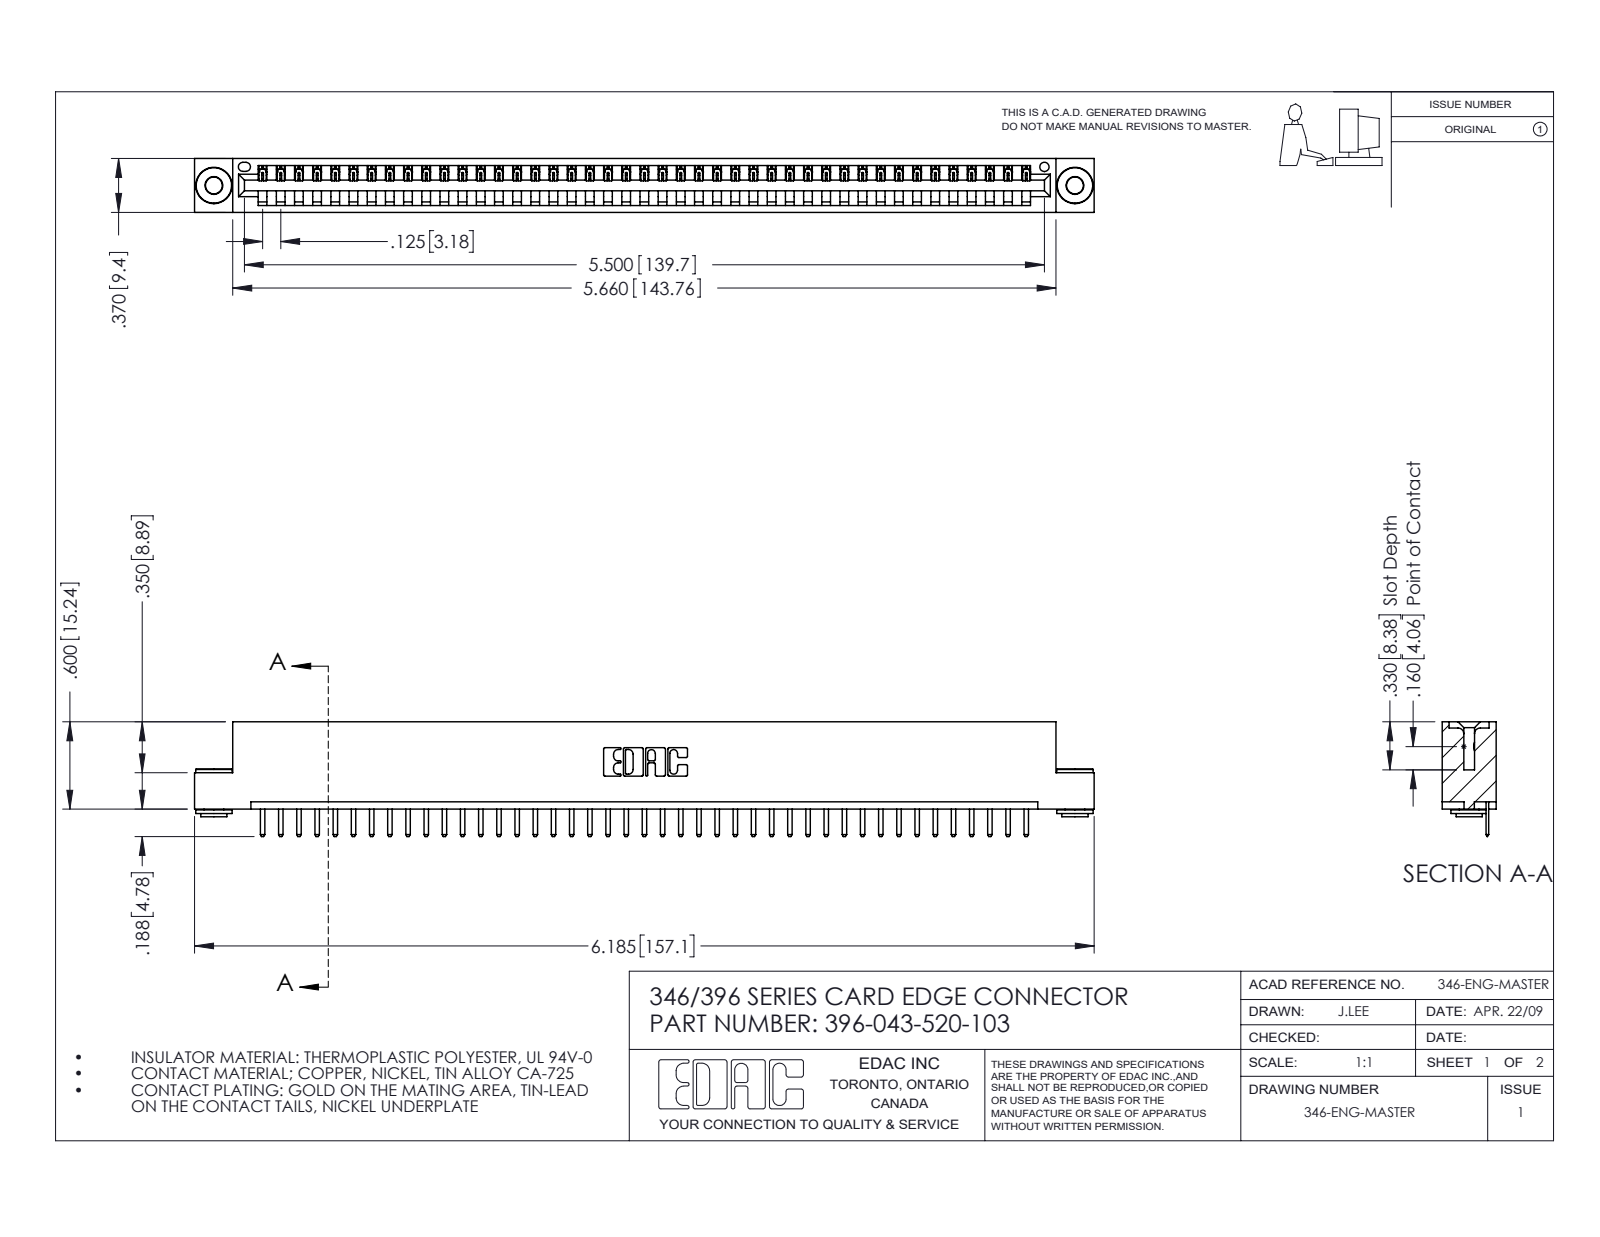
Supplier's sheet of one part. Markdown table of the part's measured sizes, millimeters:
| quantity | value |
| --- | --- |
| part name | 345-292-001_345-293-120; 346 Part_Flush Mounting Lugs - 0.156 Dia-TH; 396-043-520-103; 345-250-002_345-250-002-102 |
| STEP written by | SolidWorks 2016 (CONFIG_CONTROL_DESIGN) |
| units | millimeters |
| bodies | 46 solids, 2826 faces (1892 planar, 926 cylindrical, 8 other) |
| overall size | 157.1 × 20 × 9.4 |
| volume | 14 900 mm³ |
| surface area | 18 490 mm² |
| round holes (diameter × count) | 2.9 × 2, 4 × 2, 1.6 × 1 |
| round bosses / shafts (diameter × count) | 6.4 × 2, 4.6 × 2, 3.5 × 2 |
| partial cylindrical surfaces (radius × count) | 0.3 × 88, 0.2 × 86, 0.3 × 22, 0.2 × 6, 0.8 × 6, 0.7 × 3, 0.8 × 2, 1 × 2 |
| main face-to-face distances | 1.2, 8.2, 9.4, 6.4, 3.8, 5.6, 2.5, 4.4, 0.6, 1.8 |
| hole center spacings | 6.2, 145.1, 150.4 |
